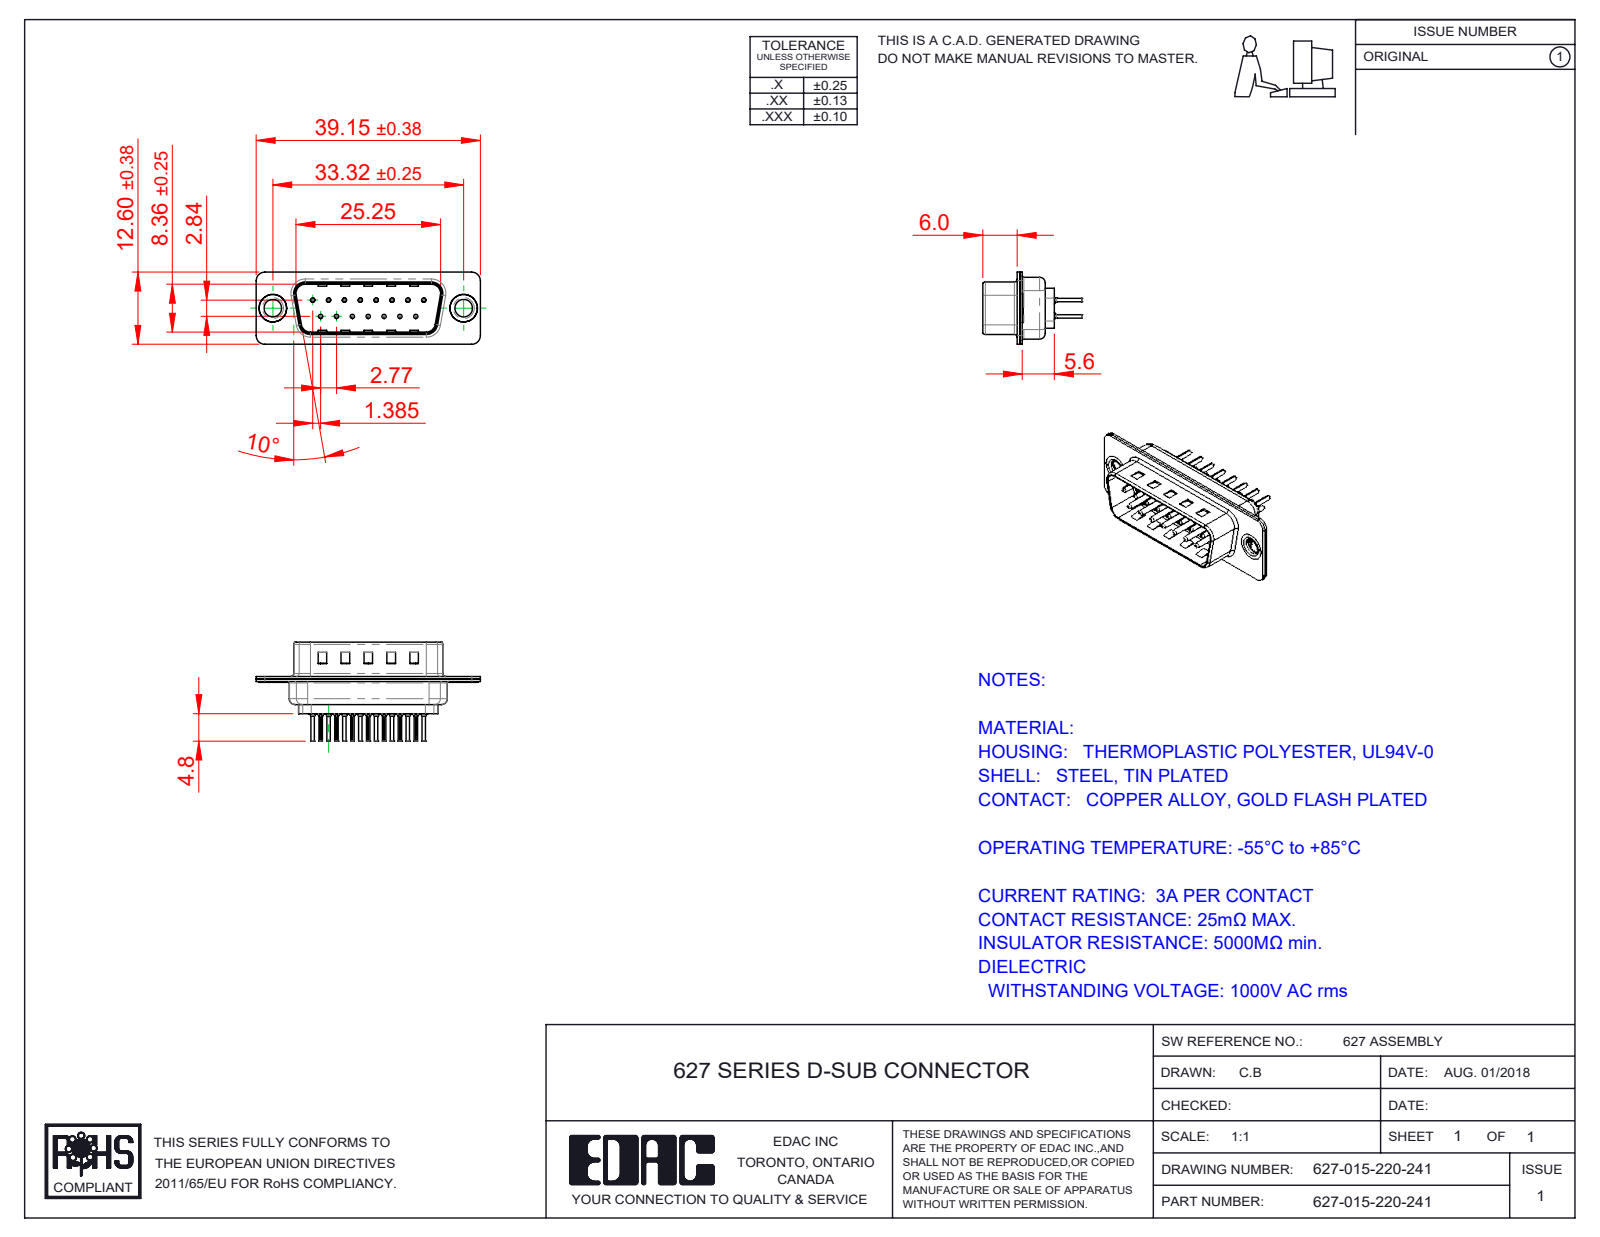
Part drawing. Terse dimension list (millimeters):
name: 627 Thru Hole Rivet; 627 Contact Row 1_20L; 627-015-220-241; 627 Housing_15 LP (+3 more)
written by: SolidWorks 2020 (CONFIG_CONTROL_DESIGN)
unit: mm
bodies: 20 solids, 1784 faces (499 planar, 672 cylindrical, 613 other)
size: 39.15 × 17.3 × 12.6
volume: 1 753 mm³; area: 5 247 mm²
holes: 15× ⌀0.2, 15× ⌀0.35, 15× ⌀1.1, 15× ⌀1.6, 2× ⌀3.05, 2× ⌀4, 2× ⌀4.8
bosses: 15× ⌀2, 15× ⌀1.5, 15× ⌀0.75, 15× ⌀0.6, 2× ⌀5, 2× ⌀4.9, 2× ⌀3.55
rounds: 30× R0.1, 16× R1.5, 12× R2, 8× R0.5, 8× R1.6, 4× R0.25, 4× R0.6, 4× R0.65
face distances: 0.4, 0.45, 0.9, 0.82, 9.58, 8.76, 1.5, 1.4, 0.5, 6.5
hole spacings: 3.16, 2.77, 5.54, 8.31, 11.08, 5.03, 5.04, 7.48
